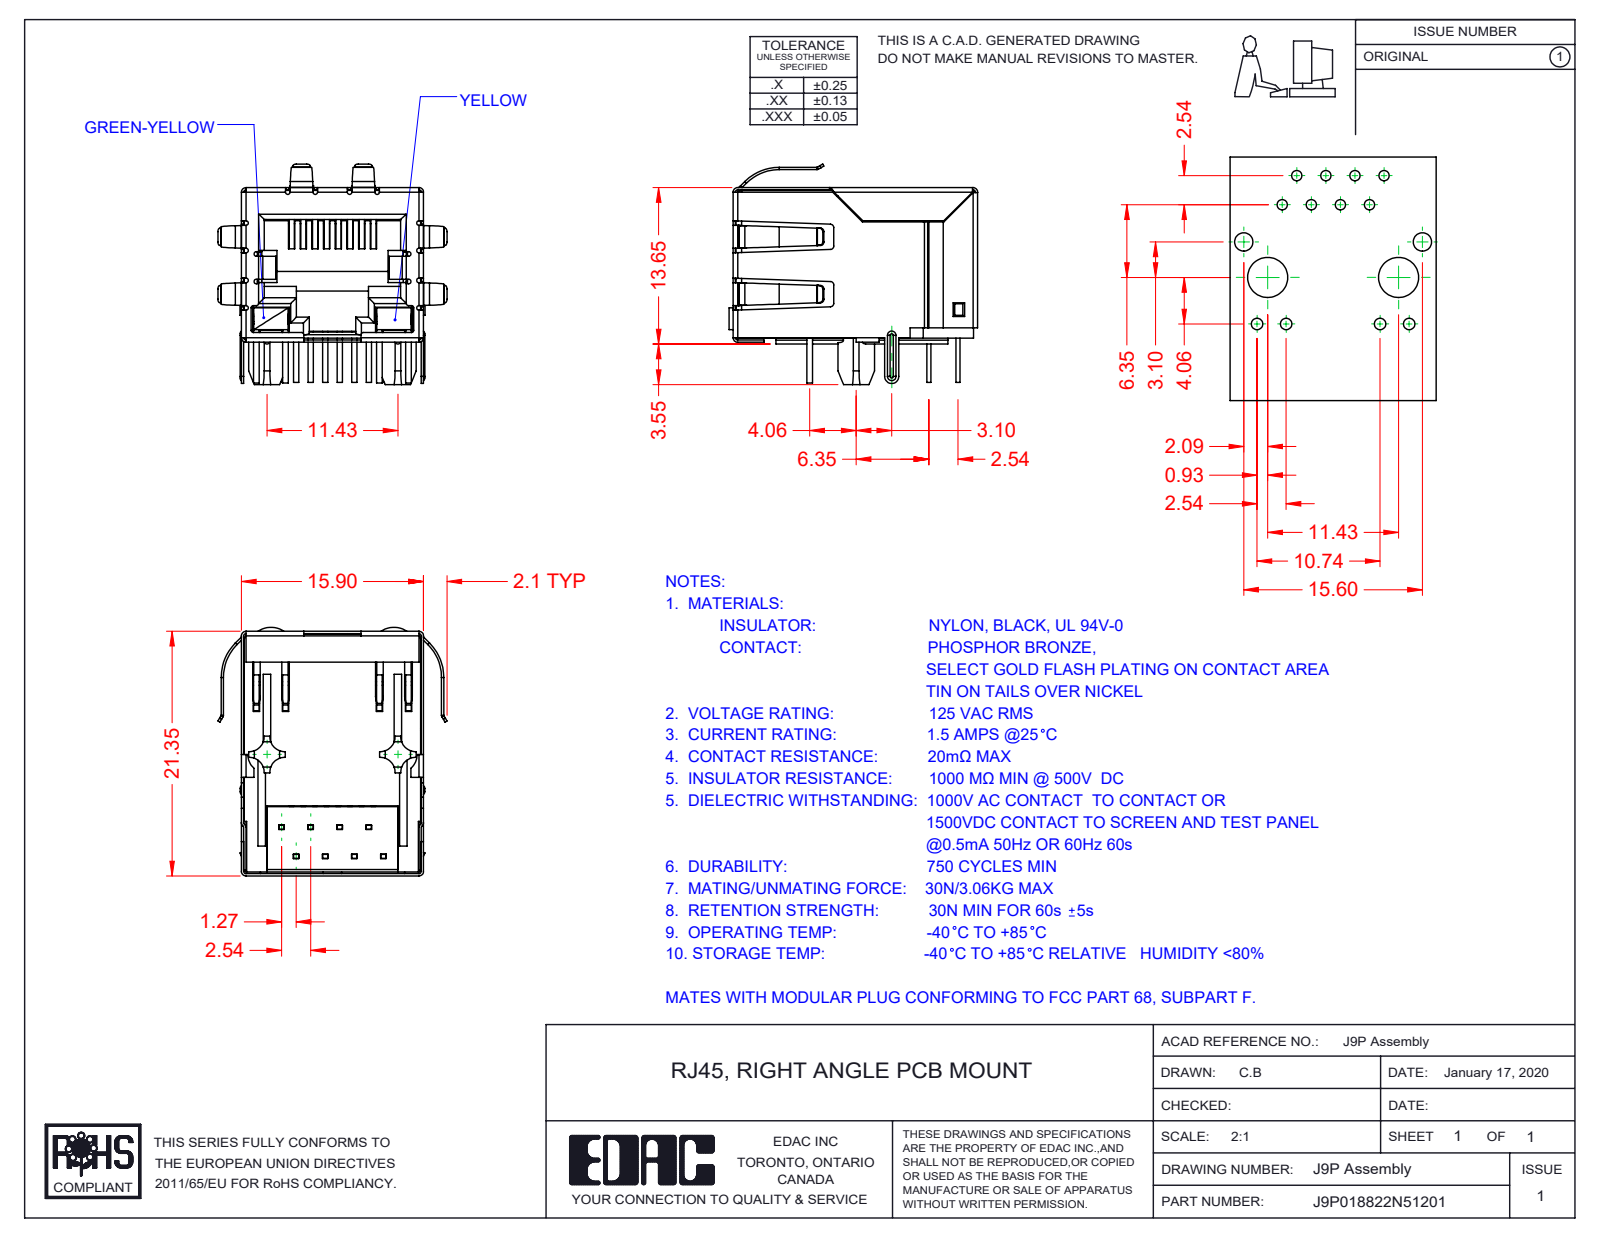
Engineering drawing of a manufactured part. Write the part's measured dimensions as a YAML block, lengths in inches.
part_name: "9P-LED Assembly; 9P-LED Contact Lock; J9P018822N51202; 9P-LED Insulator (+4 more)"
step_written_by: "SolidWorks 2016 (CONFIG_CONTROL_DESIGN)"
units: inches
bodies: {solids: 13, faces: 1474, planar: 1042, cylindrical: 338, other: 94}
overall_size: [0.854, 0.787, 0.758]
volume: 0.164
surface_area: 11.65
partial_cylinders:
  - {radius: 0.008, count: 39}
  - {radius: 0.02, count: 22}
  - {radius: 0.012, count: 20}
  - {radius: 0.016, count: 16}
  - {radius: 0.051, count: 8}
  - {radius: 0.009, count: 5}
  - {radius: 0.004, count: 4}
  - {radius: 0.012, count: 4}
face_to_face_distances: [0.608, 0.618, 0.616, 0.014, 0.021, 0.61, 0.487, 0.024, 0.055, 0.023]
